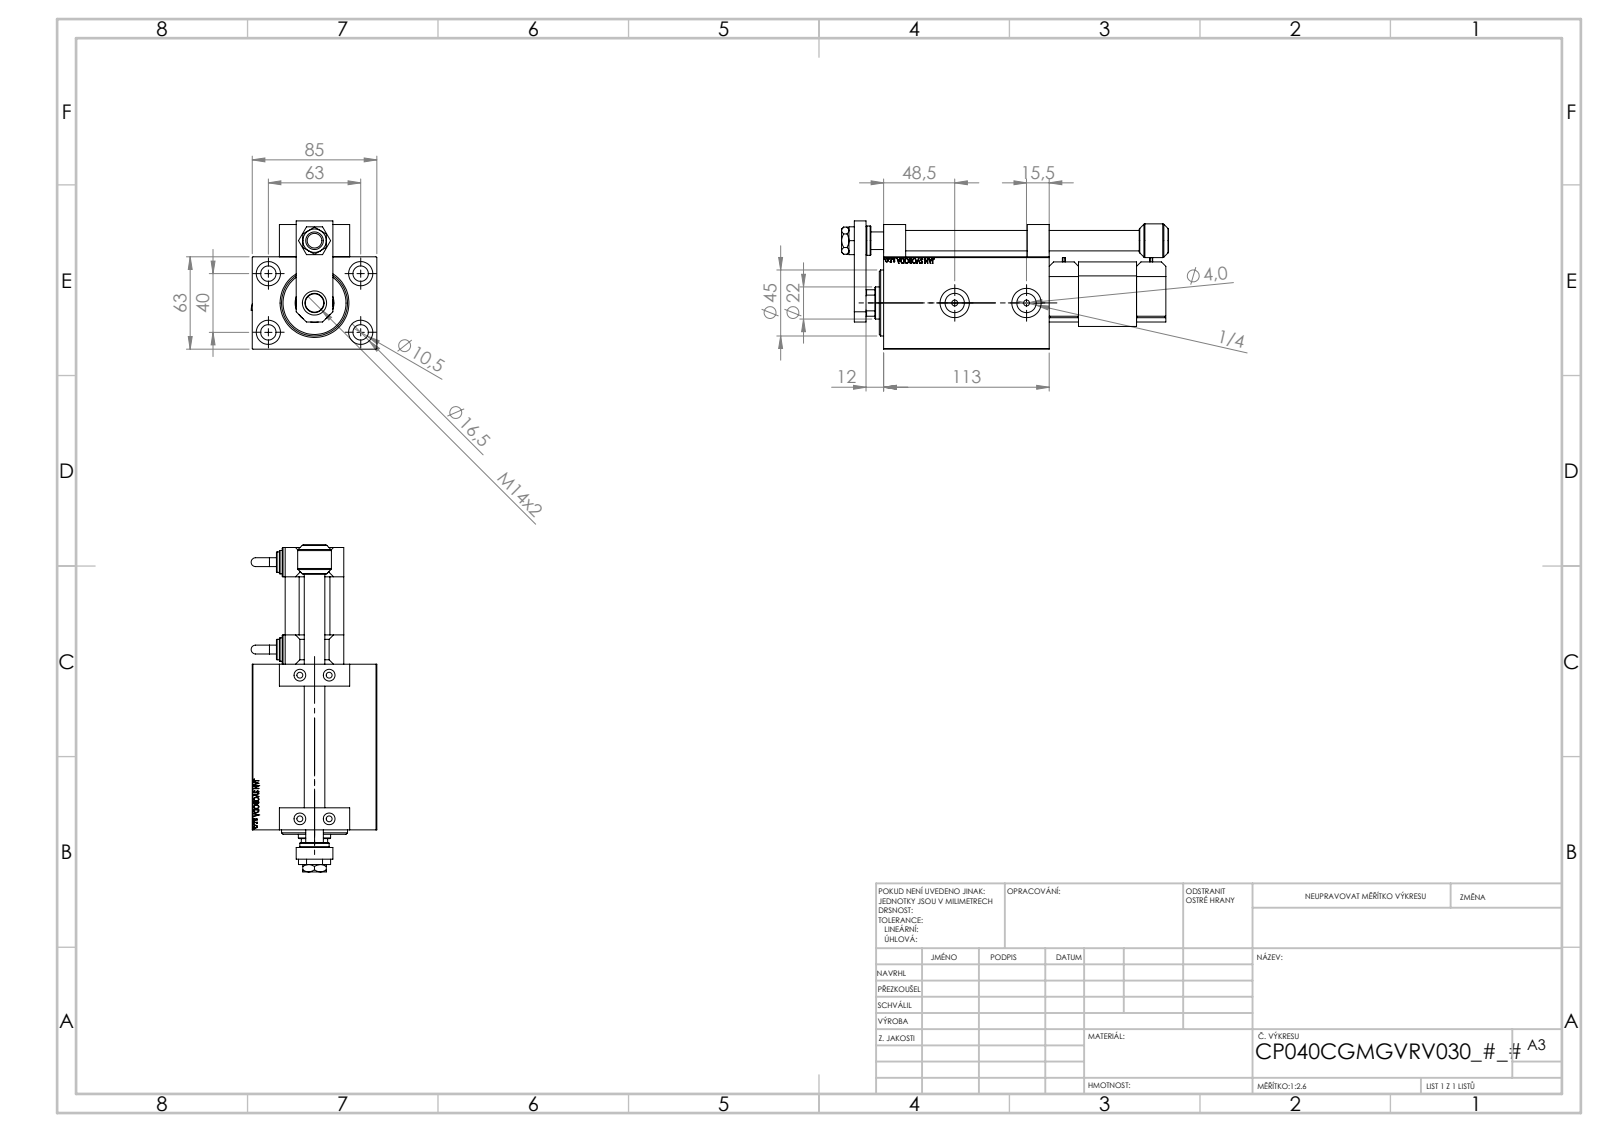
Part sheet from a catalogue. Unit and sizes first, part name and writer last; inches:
Units: inches
Overall size (bounding box): 8.783 × 3.445 × 3.376
Round holes (diameter × count): ⌀0.157 ×8, ⌀0.65 ×5, ⌀0.315 ×4, ⌀0.413 ×4, ⌀0.383 ×2, ⌀0.518 ×2, ⌀0.551 ×2, ⌀0.591 ×2, ⌀0.787 ×2, ⌀0.472 ×1, ⌀0.492 ×1, ⌀0.512 ×1
Round bosses / shafts (diameter × count): ⌀0.787 ×3, ⌀0.63 ×2, ⌀0.551 ×2, ⌀0.236 ×2, ⌀0.906 ×1
Partial cylindrical surfaces — rounded edges, fillets, slot ends (radius × count): R0.118 ×1, R0.413 ×1
Main face-to-face distances: 2.48, 3.346, 0.787, 4.449, 2.461, 0.886, 5.236, 2.346, 0.472, 1.732
Hole centre spacings: 1.469, 0.787, 1.524, 1.547, 1.575, 2.48, 2.756, 2.791
Volume: 44.8 in³ · Surface area: 235 in²
Bodies: 14 solids, 1110 faces (525 planar, 132 cylindrical, 453 other)
Part name (STEP PRODUCT): SWITCH DIM W_B; V450CP_VC_B; SWITCH_P_FRONT_BACK; MIDDLE (+7 more)
STEP written by: SolidWorks 2019 (CONFIG_CONTROL_DESIGN)
